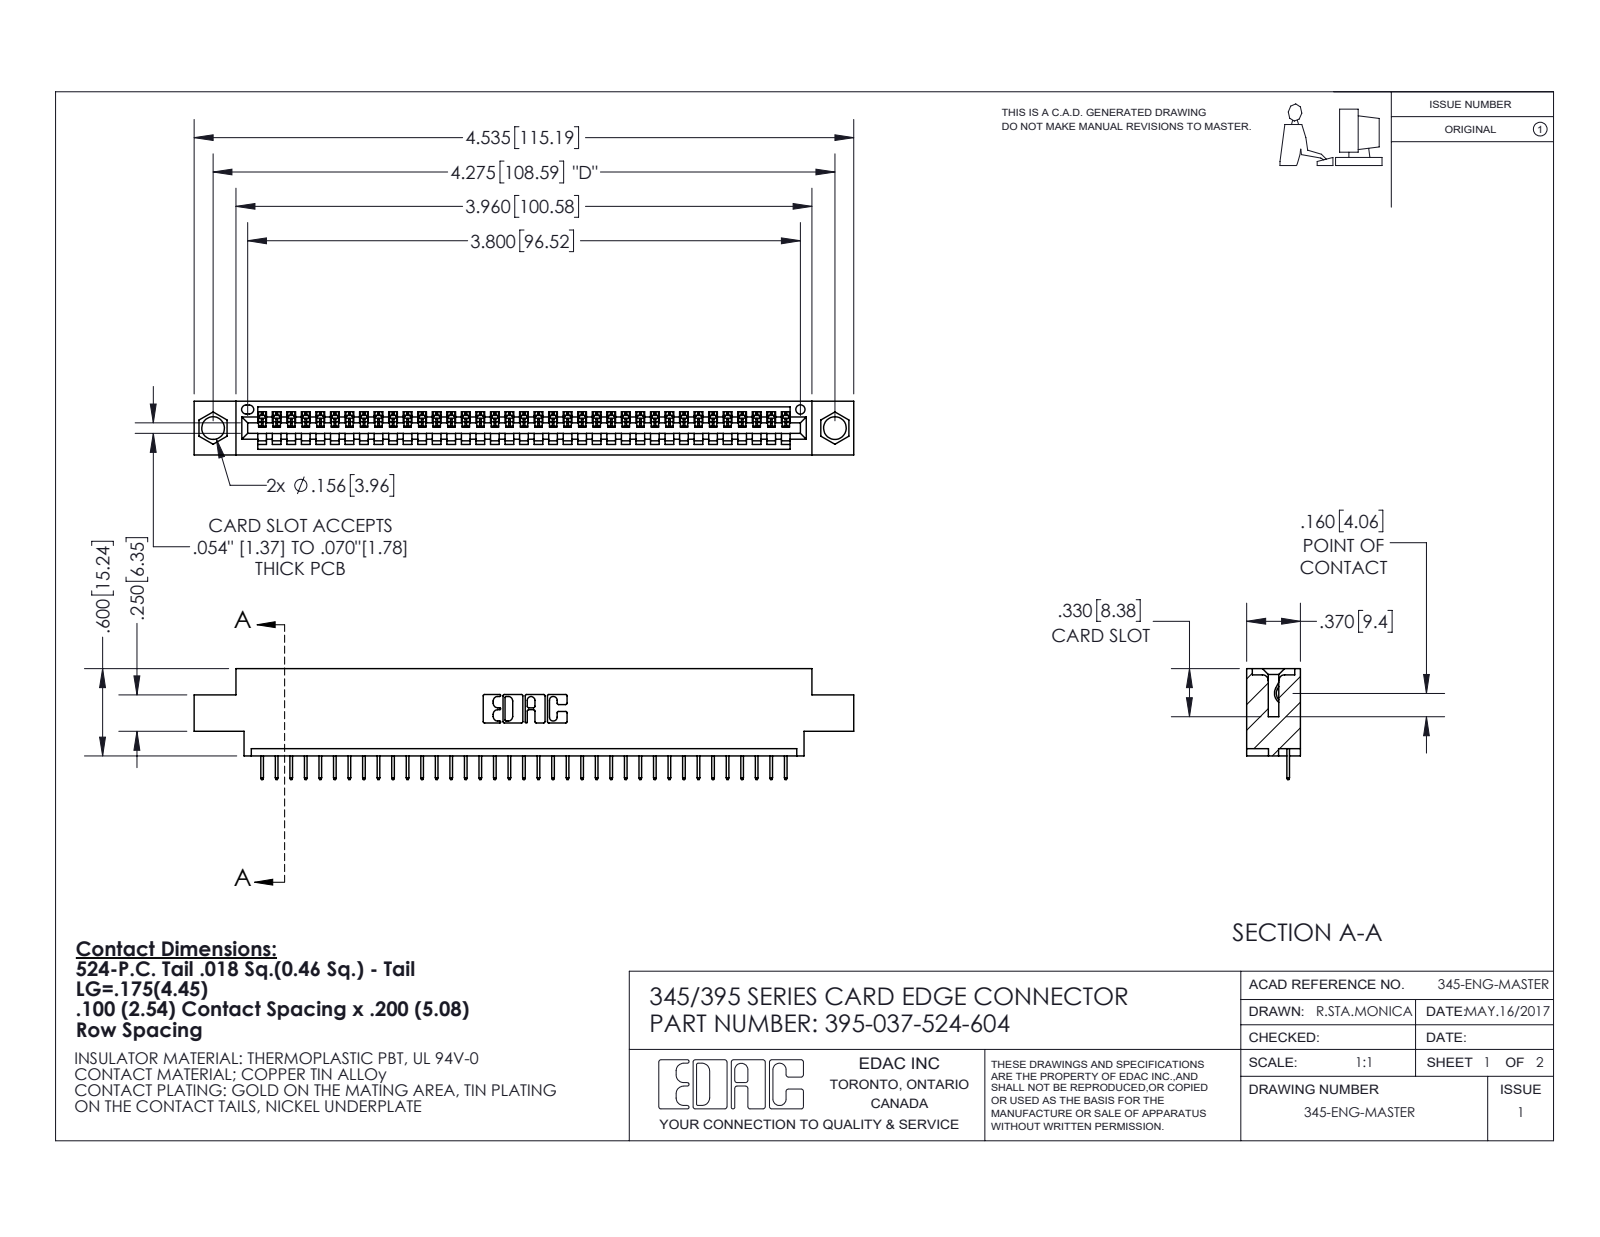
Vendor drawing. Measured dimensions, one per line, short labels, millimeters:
name: 395-037-524-604; 345 Part_0.170 Offset - 0.156 Dia-TI; 345-292-001_345-293-124
written by: SolidWorks 2020 (CONFIG_CONTROL_DESIGN)
unit: mm
bodies: 38 solids, 2438 faces (1800 planar, 638 cylindrical, 0 other)
size: 115.2 × 19.4 × 9.4
volume: 10 500 mm³; area: 13 430 mm²
holes: 2× ⌀4, 1× ⌀1.6
rounds: 74× R0.2, 22× R0.3, 6× R0.2, 6× R0.8, 3× R0.7, 2× R0.8, 2× R1, 1× R0.4
face distances: 1.8, 7.6, 9.4, 5.1, 2.5, 6.9, 0.6, 5.7, 1.8, 4.4
hole spacings: 6.9, 102.6, 108.6
